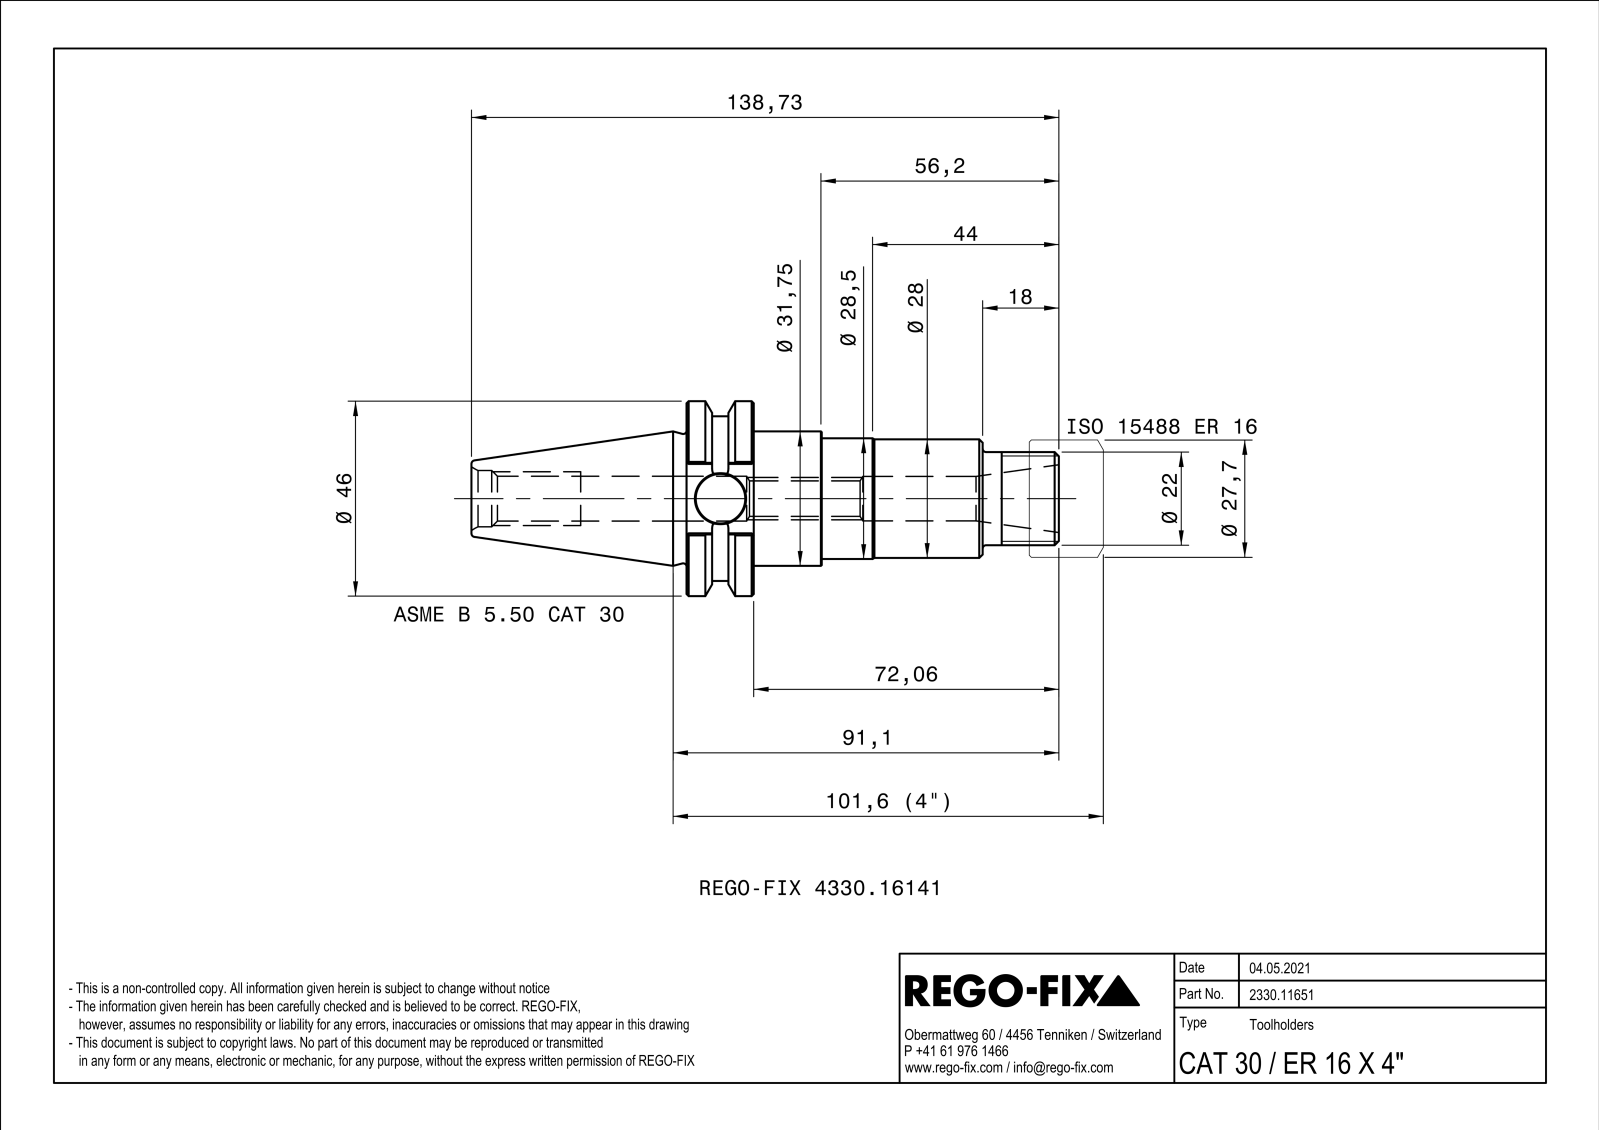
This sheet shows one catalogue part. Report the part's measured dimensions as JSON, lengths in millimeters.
{"part_name": "0007563", "step_written_by": "SIEMENS PLM Software Solid Edge ST10 (AUTOMOTIVE_DESIGN)", "units": "millimeters", "bodies": {"solids": 1, "faces": 101, "planar": 37, "cylindrical": 23, "other": 41}, "overall_size": [138.73, 46.03, 42.63], "volume_mm3": 77647, "surface_area_mm2": 19846, "round_holes": [[8.38, 1], [10.5, 1], [10.58, 1], [10.58, 1], [11.7, 1], [13.3, 1]], "round_bosses_or_shafts": [[31.75, 1], [28.5, 1], [28, 1], [22, 1]], "partial_cylinders_radius": [[0.5, 4], [19.44, 1], [23.02, 1]], "face_to_face_distances": [15.87, 34.63, 54.06, 69.93, 18, 72.06, 87.93, 16.38, 81.89, 63.89]}
